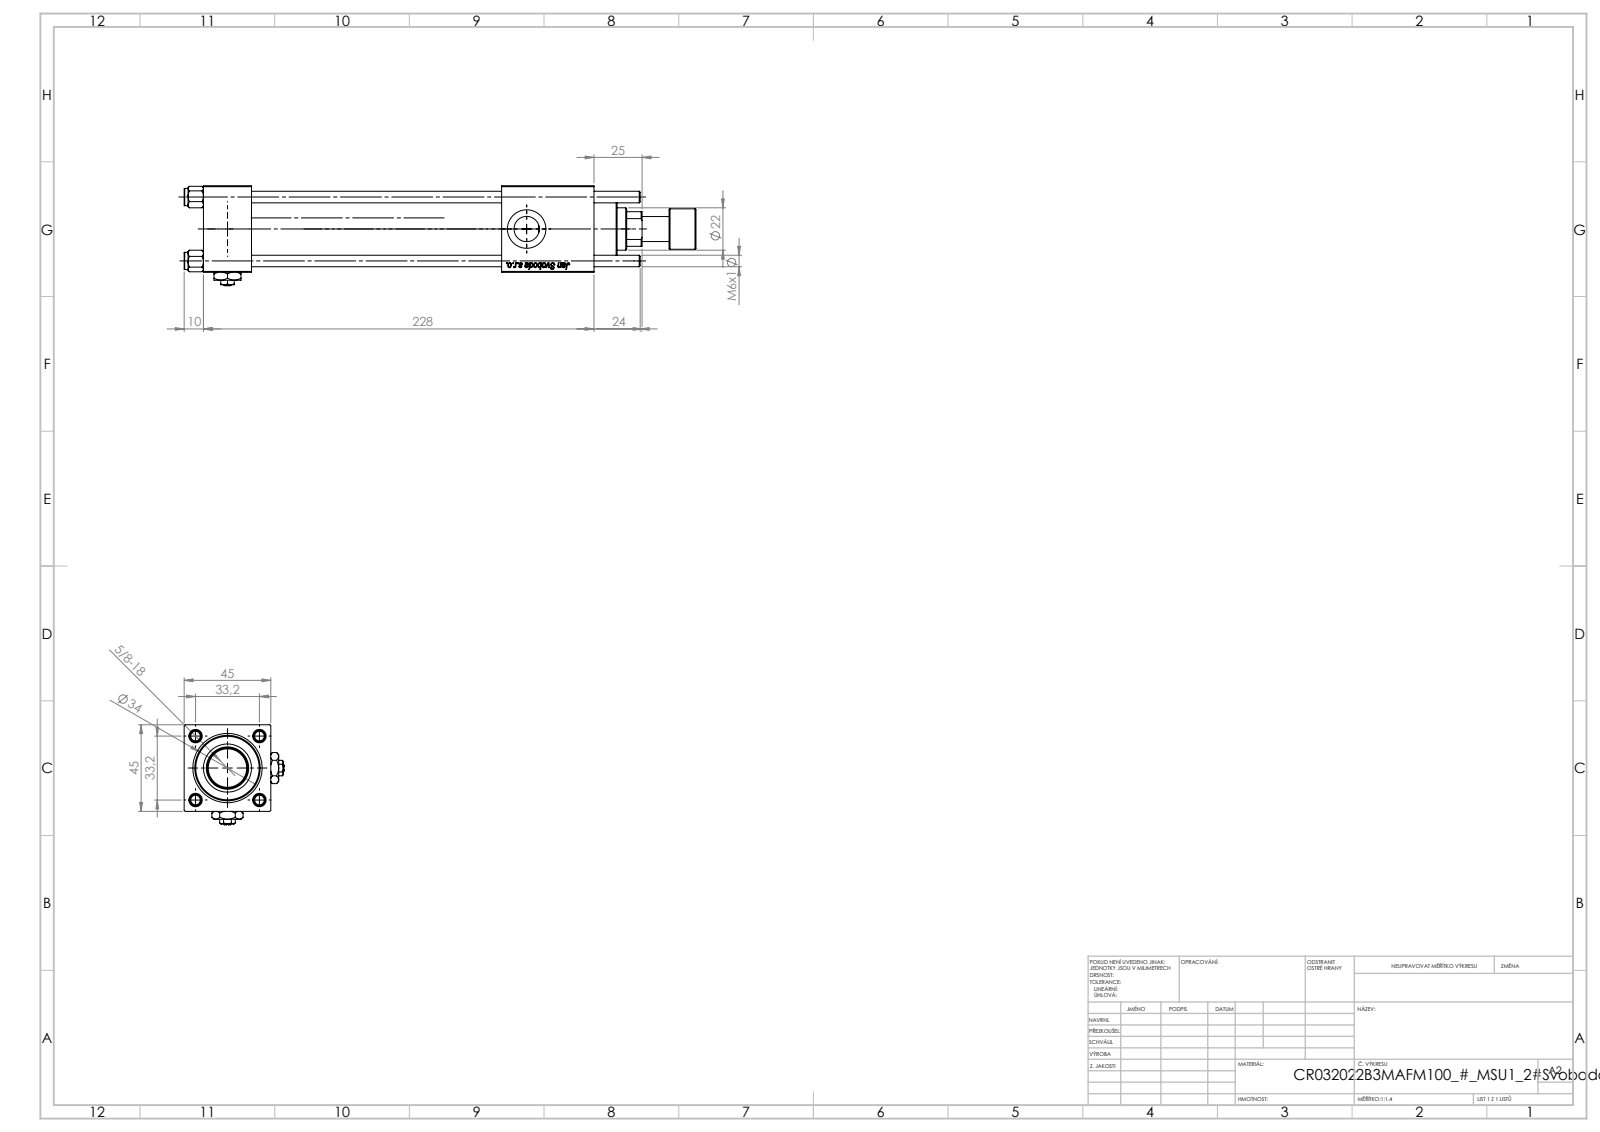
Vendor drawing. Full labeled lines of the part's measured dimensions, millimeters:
Part name (STEP PRODUCT): V215CR_B-1; NUT_M5_B; V215_VC_A; Zatka_pro_OIL_PORT (+3 more)
STEP written by: SolidWorks 2019 (CONFIG_CONTROL_DESIGN)
Units: millimetres
Bodies: 14 solids, 1267 faces (479 planar, 94 cylindrical, 694 other)
Overall size (bounding box): 266 × 52 × 52
Volume: 284 958 mm³ · Surface area: 110 001 mm²
Round holes (diameter × count): ⌀6 ×4, ⌀7 ×2, ⌀13.16 ×2, ⌀20 ×2, ⌀10.5 ×1, ⌀13 ×1, ⌀22 ×1, ⌀24 ×1, ⌀25 ×1, ⌀32 ×1, ⌀33 ×1
Round bosses / shafts (diameter × count): ⌀9 ×4, ⌀38 ×1, ⌀34 ×1, ⌀21 ×1, ⌀13 ×1
Main face-to-face distances: 45, 25, 203, 155, 130, 178, 48, 44.8, 174.3, 149.3
Hole centre spacings: 23.48, 33.2, 46.95
